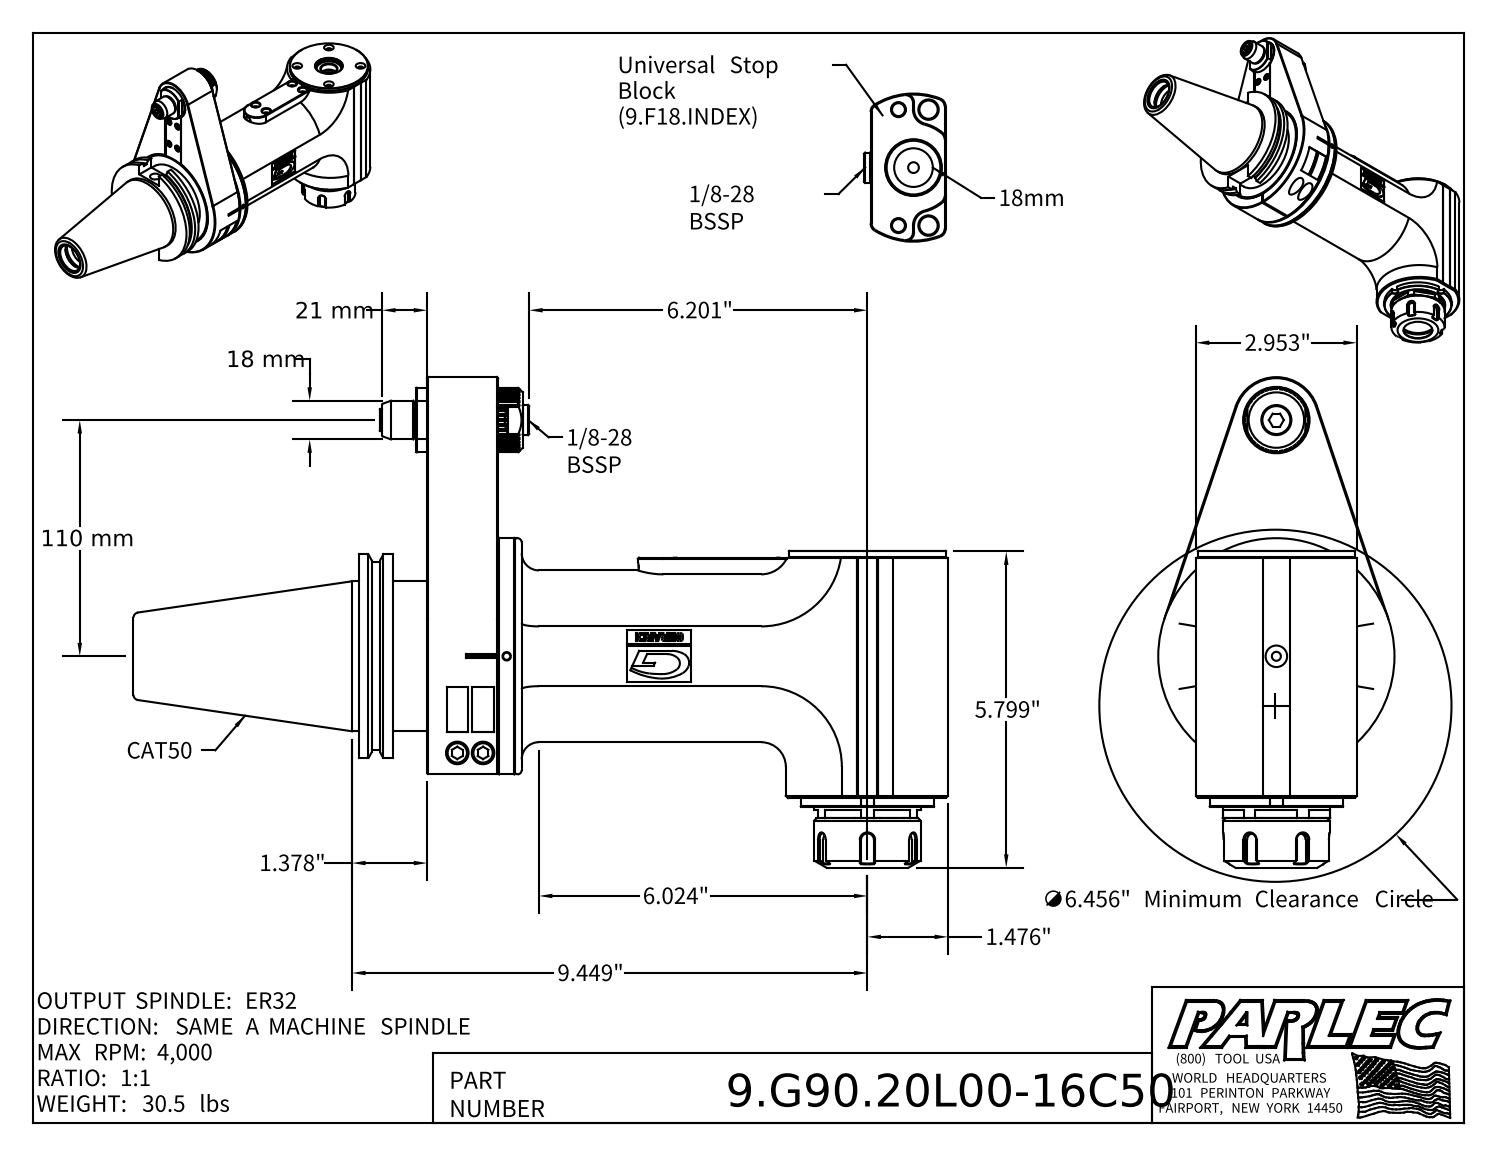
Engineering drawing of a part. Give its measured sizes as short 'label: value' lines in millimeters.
name: 9.G90.20L00-16C50; 9_G90_20L00; 9_GA2_451_1 (Type 2, Cat50, 110mm, CLASSIC)
written by: Autodesk Inventor 2022 (AUTOMOTIVE_DESIGN)
unit: mm
bodies: 4 solids, 961 faces (495 planar, 206 cylindrical, 260 other)
size: 379.3 × 228.5 × 110
volume: 2 142 000 mm³; area: 229 200 mm²
holes: 11× ⌀5, 9× ⌀3.3, 8× ⌀4.5, 4× ⌀6, 4× ⌀8, 4× ⌀8.5, 2× ⌀4, 2× ⌀4.2, 2× ⌀7, 2× ⌀10.5, 2× ⌀11, 1× ⌀14
bosses: 4× ⌀10, 2× ⌀6, 1× ⌀110, 1× ⌀102, 1× ⌀98.4, 1× ⌀91.3, 1× ⌀89.5, 1× ⌀80
rounds: 7× R3, 2× R2.2, 2× R8, 2× R11.9, 2× R12, 2× R40, 1× R2, 1× R2.5
face distances: 33, 8, 25, 15.9, 75, 3, 5, 23.9, 48.9, 64.8
hole spacings: 47.5, 82.3, 95, 24.6, 25.6, 29.5, 41.7, 47.5
